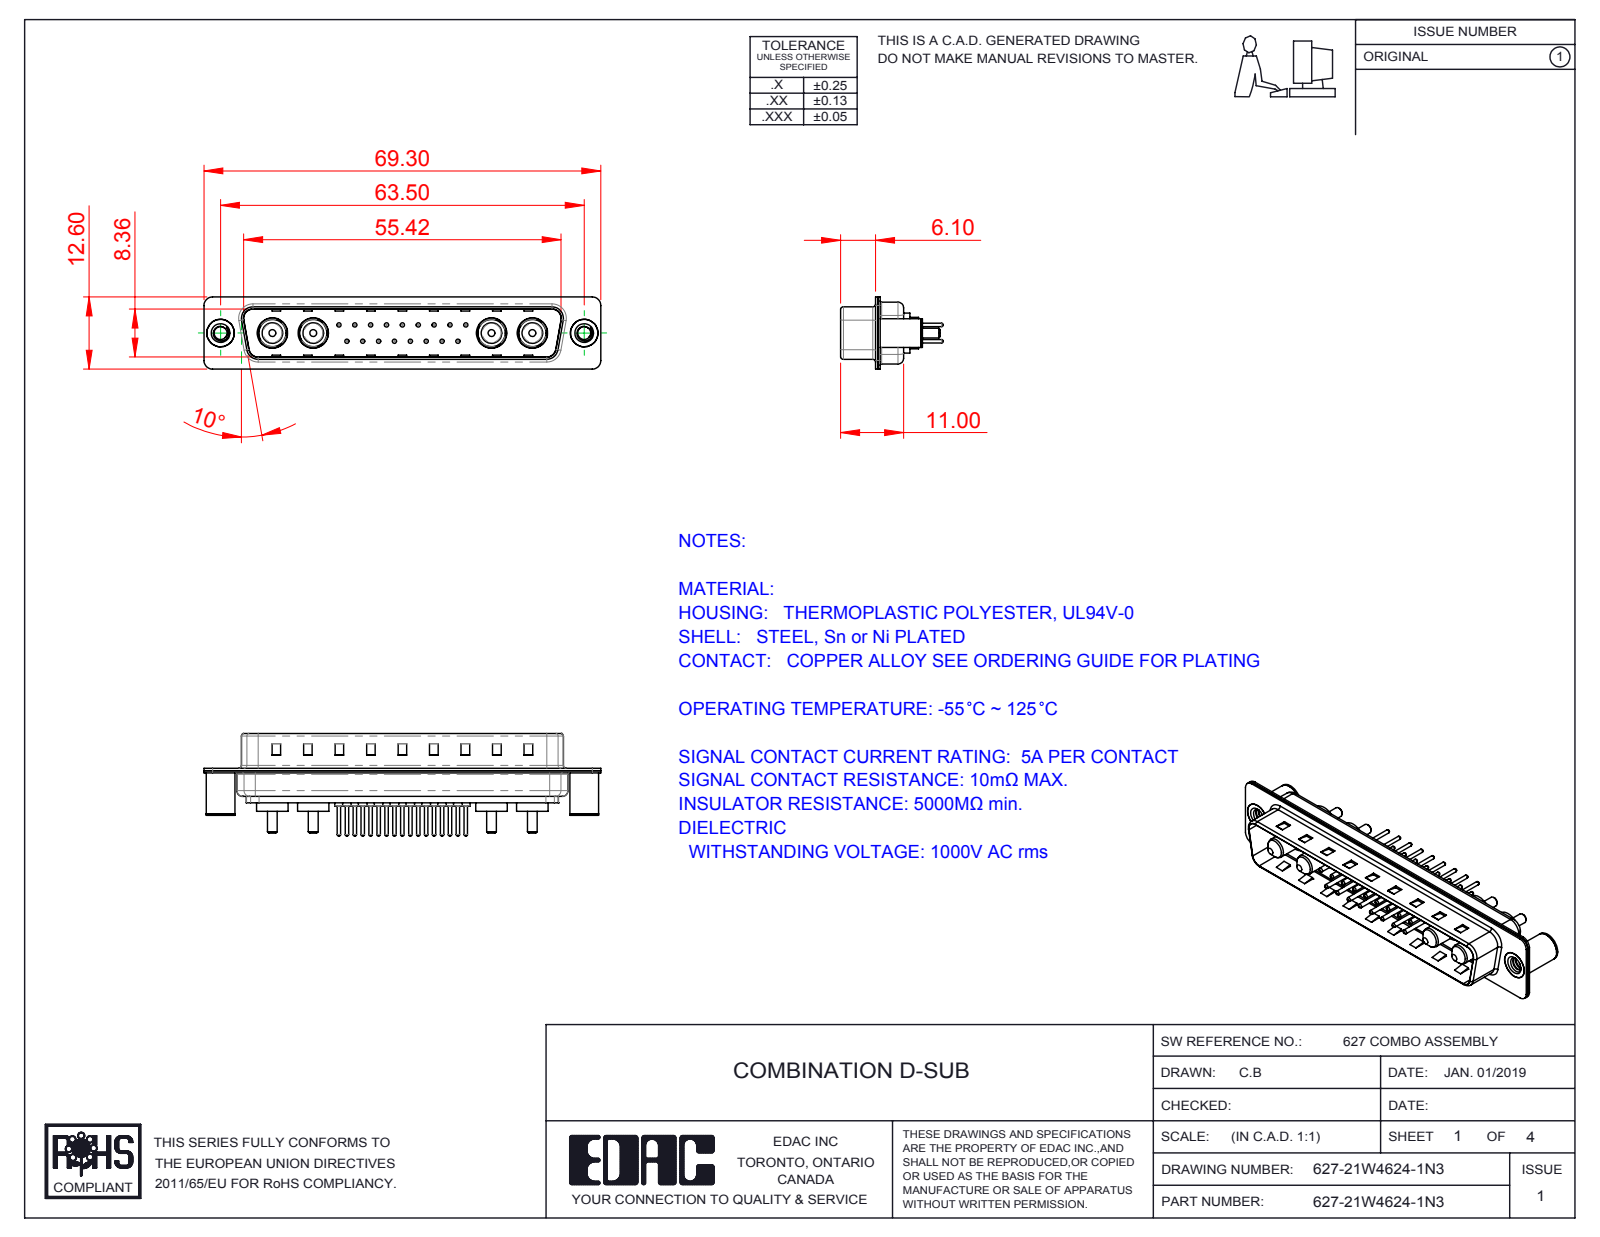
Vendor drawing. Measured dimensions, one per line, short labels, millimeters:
name: 627Combo Shell Rear_37 Contacts; 627Combo Housing_21W4; Power Pin_10A S; 627Combo Shell Front_37 Contacts (+4 more)
written by: SolidWorks 2016 (CONFIG_CONTROL_DESIGN)
unit: mm
bodies: 30 solids, 1235 faces (362 planar, 479 cylindrical, 394 other)
size: 69.3 × 17.9 × 12.6
volume: 4 106 mm³; area: 9 350 mm²
holes: 17× ⌀0.75, 17× ⌀1.6, 17× ⌀2, 4× ⌀4.85, 4× ⌀5.3, 2× ⌀2.26, 2× ⌀3.26, 2× ⌀4, 2× ⌀4.8
bosses: 17× ⌀1.5, 17× ⌀0.6, 4× ⌀5.5, 4× ⌀5.2, 4× ⌀4.75, 4× ⌀3.75, 4× ⌀3.6, 4× ⌀1.7
rounds: 16× R1.5, 12× R2, 8× R0.5, 8× R1.6, 4× R0.25, 4× R0.6, 4× R0.65, 4× R0.9
face distances: 0.4, 0.82, 9.58, 8.76, 1.5, 5.6, 1.22, 9.98, 0.42, 9.18
hole spacings: 3.16, 2.77, 5.54, 8.31, 5.03, 5.04, 7.49, 10.11
